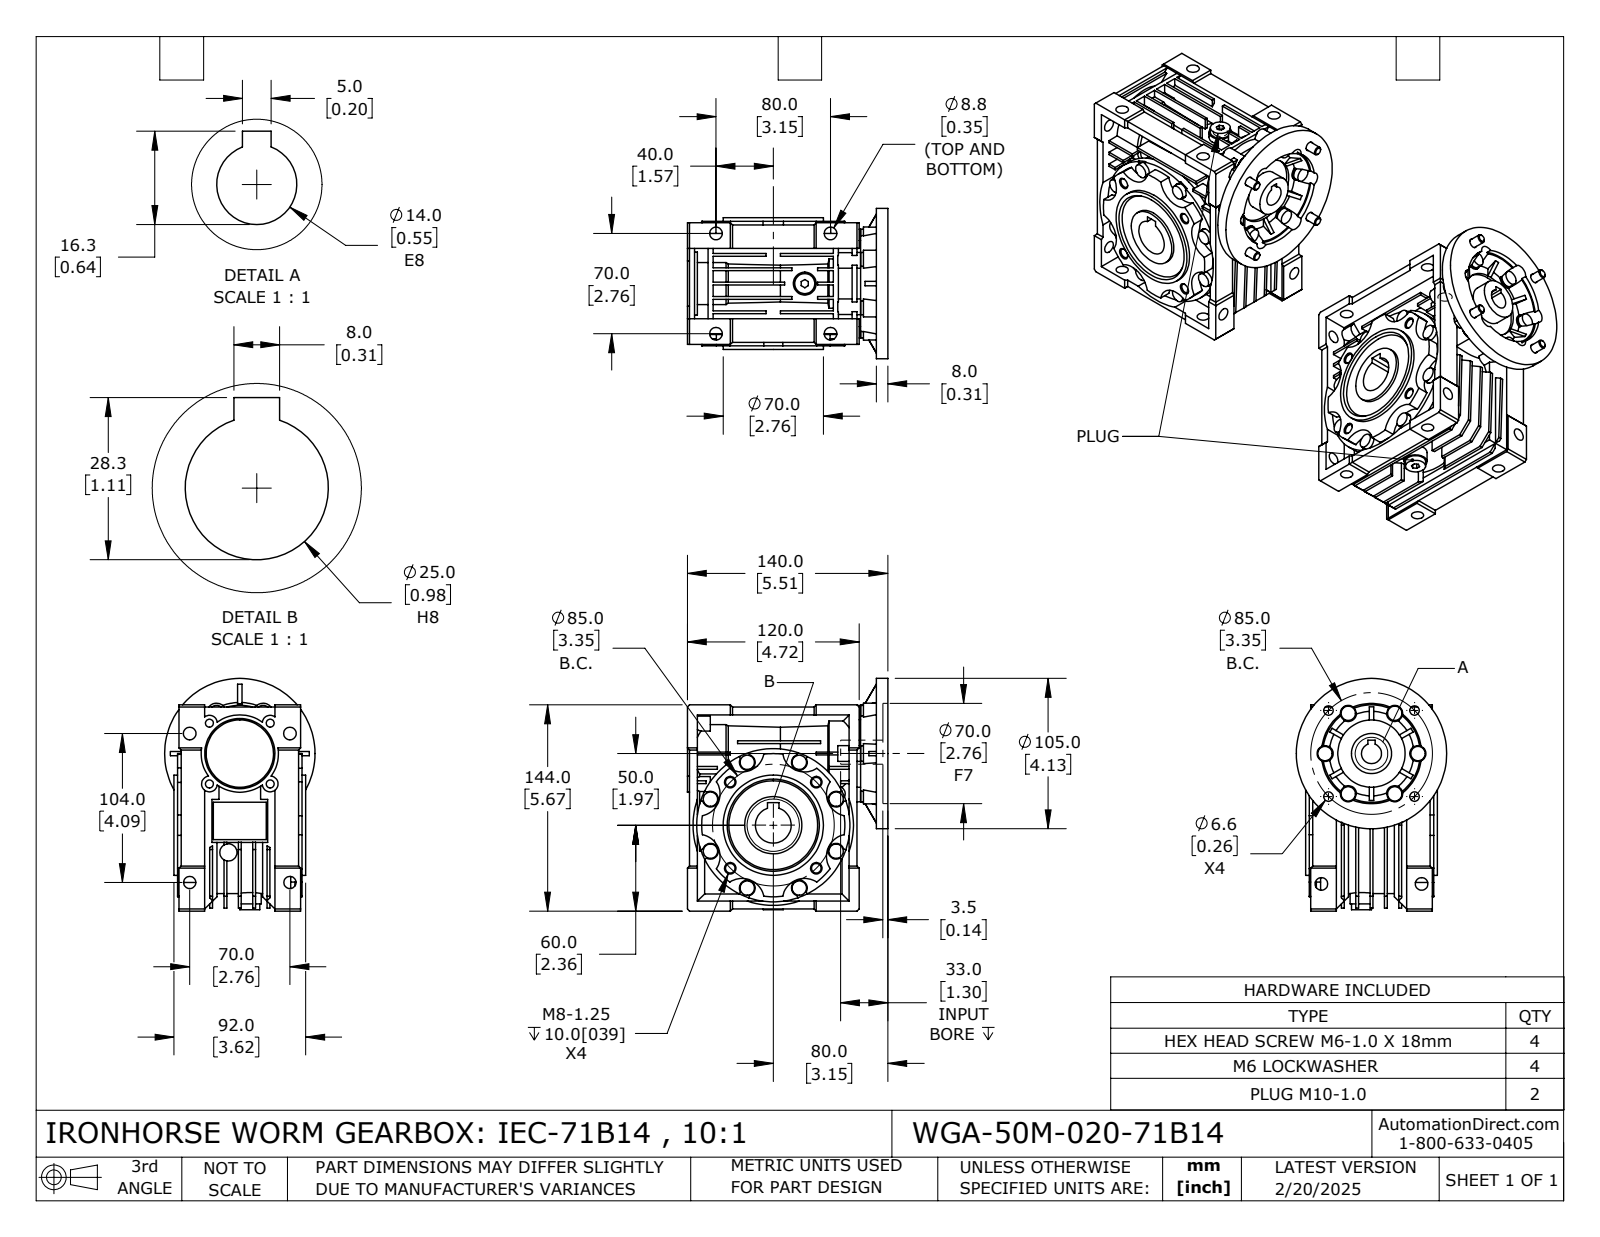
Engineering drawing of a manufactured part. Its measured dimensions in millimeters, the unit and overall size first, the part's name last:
Units: millimetres
Overall size (bounding box): 162.5 × 148.5 × 105
Round holes (diameter × count): ⌀8.8 ×8, ⌀8.5 ×6, ⌀5.55 ×4, ⌀6.1 ×4, ⌀6.6 ×4, ⌀6.65 ×2, ⌀6.65 ×2, ⌀9 ×2, ⌀14 ×1, ⌀15 ×1, ⌀25 ×1, ⌀28 ×1
Round bosses / shafts (diameter × count): ⌀10 ×14, ⌀12.2 ×4, ⌀6 ×4, ⌀16 ×2, ⌀14 ×2, ⌀9.8 ×2, ⌀8.3 ×2, ⌀107 ×1
Partial cylindrical surfaces — rounded edges, fillets, slot ends (radius × count): R5.5 ×18, R6 ×8, R15 ×8, R15.5 ×8, R5.75 ×6, R7 ×6, R20.76 ×1, R35 ×1
Main face-to-face distances: 8, 2, 10, 7, 1.5, 5.5, 20, 12, 55, 35
Hole centre spacings: 42.5, 52.02, 60.1, 70, 12.5, 30, 42.42, 72.49
Volume: 1 065 000 mm³ · Surface area: 235 209 mm²
Bodies: 15 solids, 1132 faces (615 planar, 372 cylindrical, 145 other)
Part name (STEP PRODUCT): WGA-50M-020-71B14
STEP written by: SolidWorks 2024 (CONFIG_CONTROL_DESIGN)
